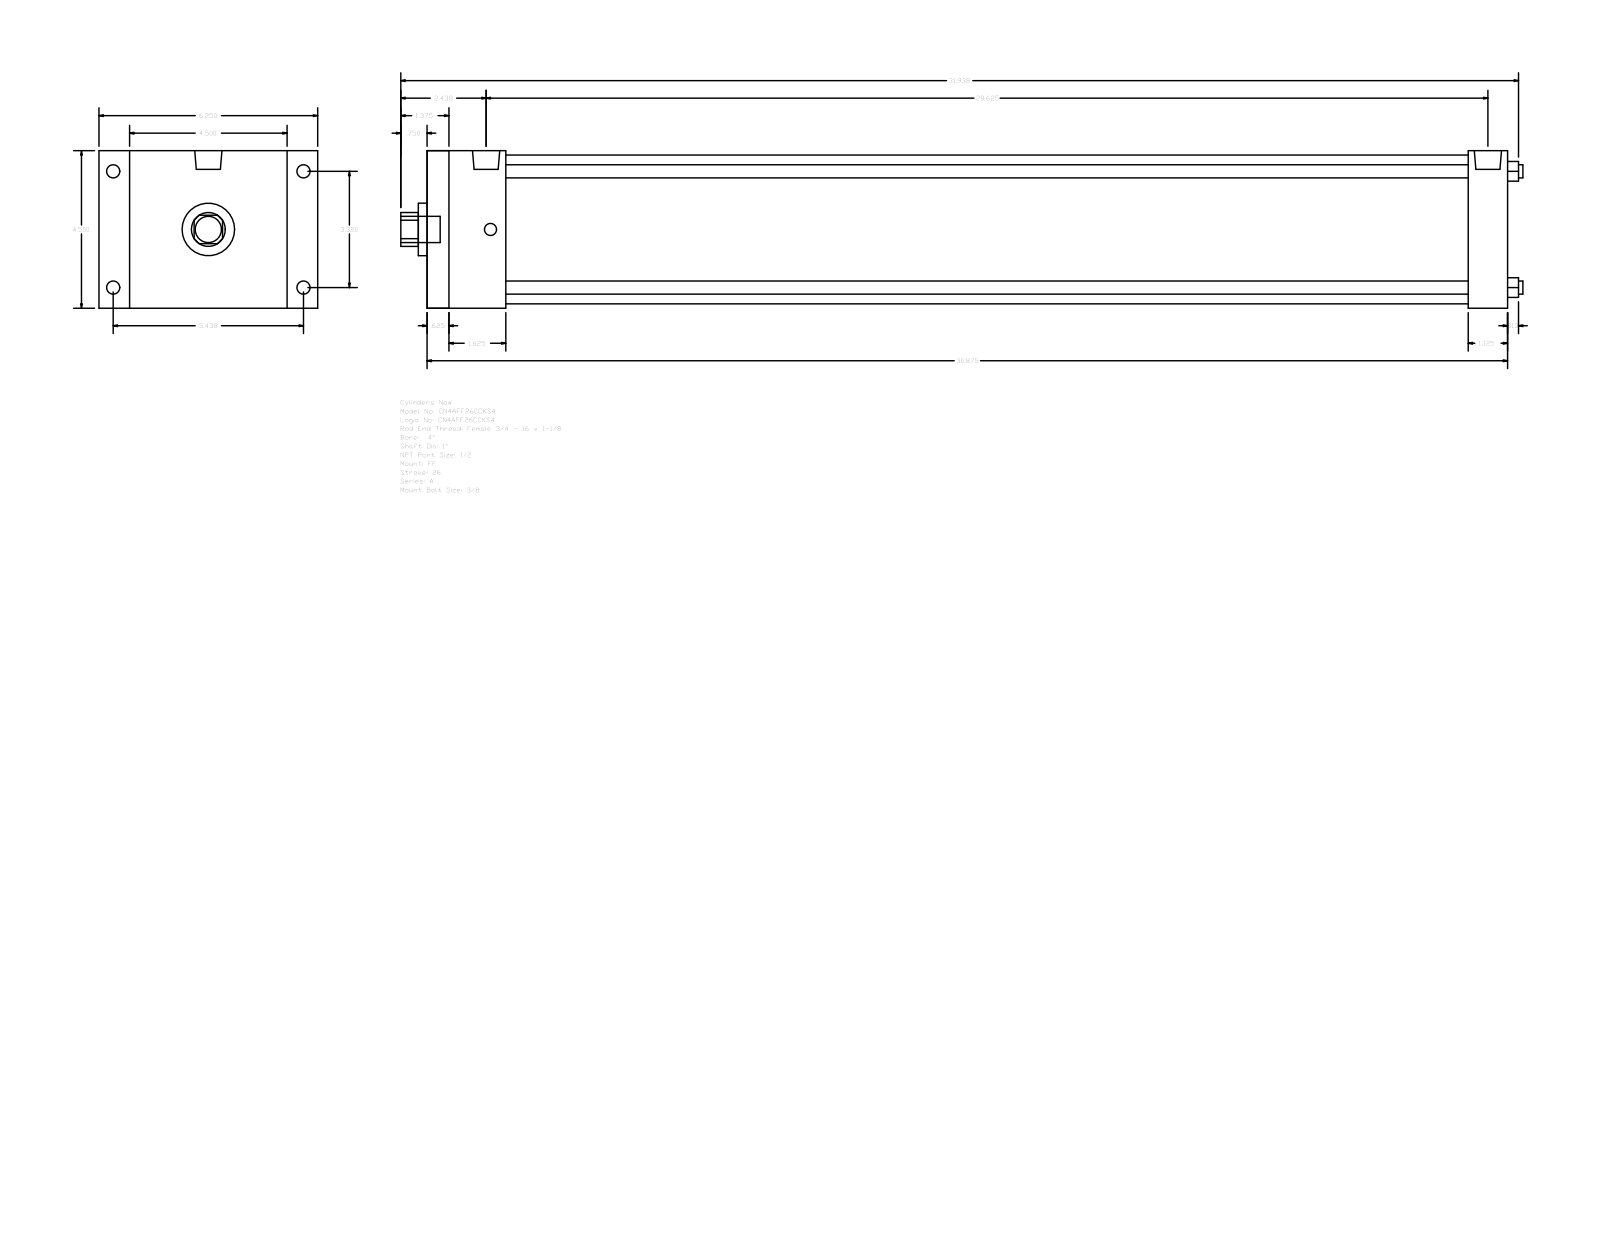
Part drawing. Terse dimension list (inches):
name: A_FF__0400_1
written by: GSSL Pune (CONFIG_CONTROL_DESIGN)
unit: in
bodies: 0 solids, 92 faces (64 planar, 28 cylindrical, 0 other)
size: 32.063 × 6.25 × 4.5
holes: 4× ⌀0.375, 1× ⌀1, 1× ⌀1.5, 1× ⌀4.25
bosses: 4× ⌀0.375, 4× ⌀0.344, 2× ⌀0.778, 1× ⌀0.75
rounds: 1× R0.484
face distances: 4.5, 30.875, 0.625, 30.25, 1.125, 0.875, 5.375, 29.75, 29.125, 2.25
hole spacings: 2.347, 3.32, 4.695
